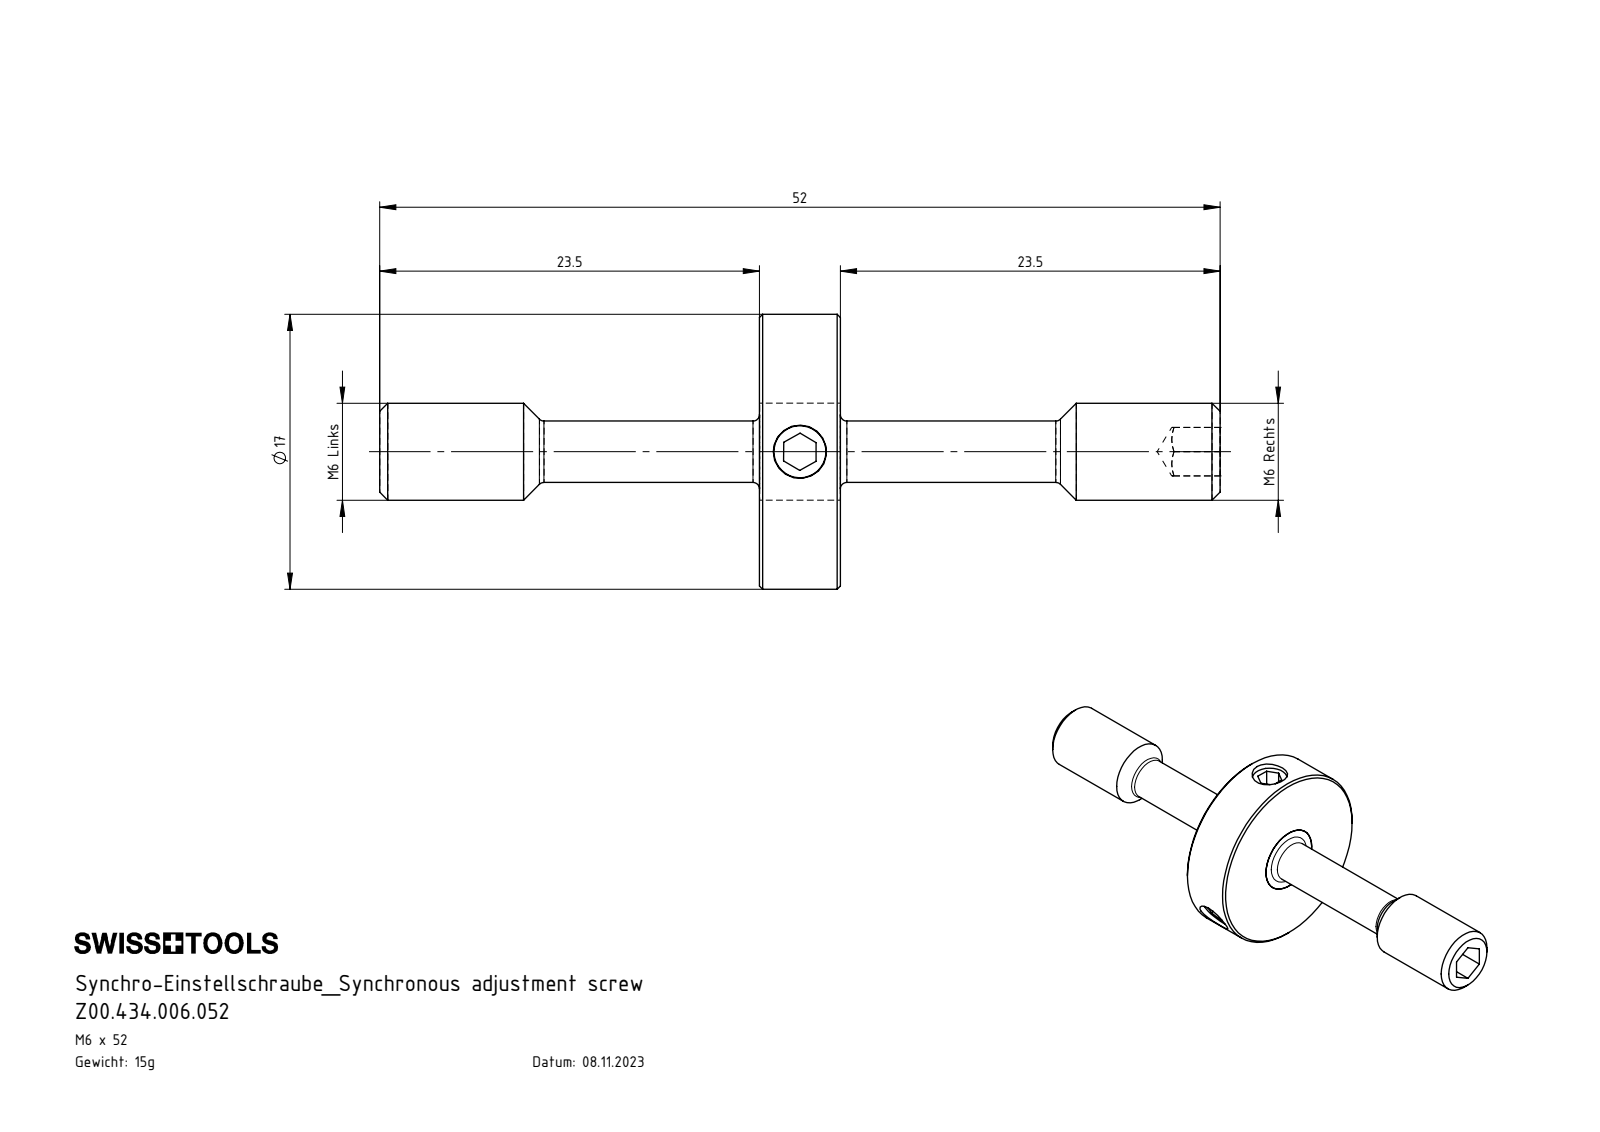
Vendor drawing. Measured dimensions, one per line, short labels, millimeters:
name: Z00.434.006.052; Z55-ER3.001.052_A; Z42-ER3.002.005_A; ISO 4026 - M4 x 5
written by: SolidWorks 2022 (AUTOMOTIVE_DESIGN)
unit: mm
bodies: 5 solids, 99 faces (39 planar, 26 cylindrical, 34 other)
size: 52 × 17 × 17
volume: 1 964 mm³; area: 2 067 mm²
holes: 3× ⌀3.3
bosses: 3× ⌀4, 1× ⌀17, 1× ⌀6, 1× ⌀3.8
face distances: 5, 23.5, 28.5, 2, 2.5, 3, 52, 25, 27, 1.5
